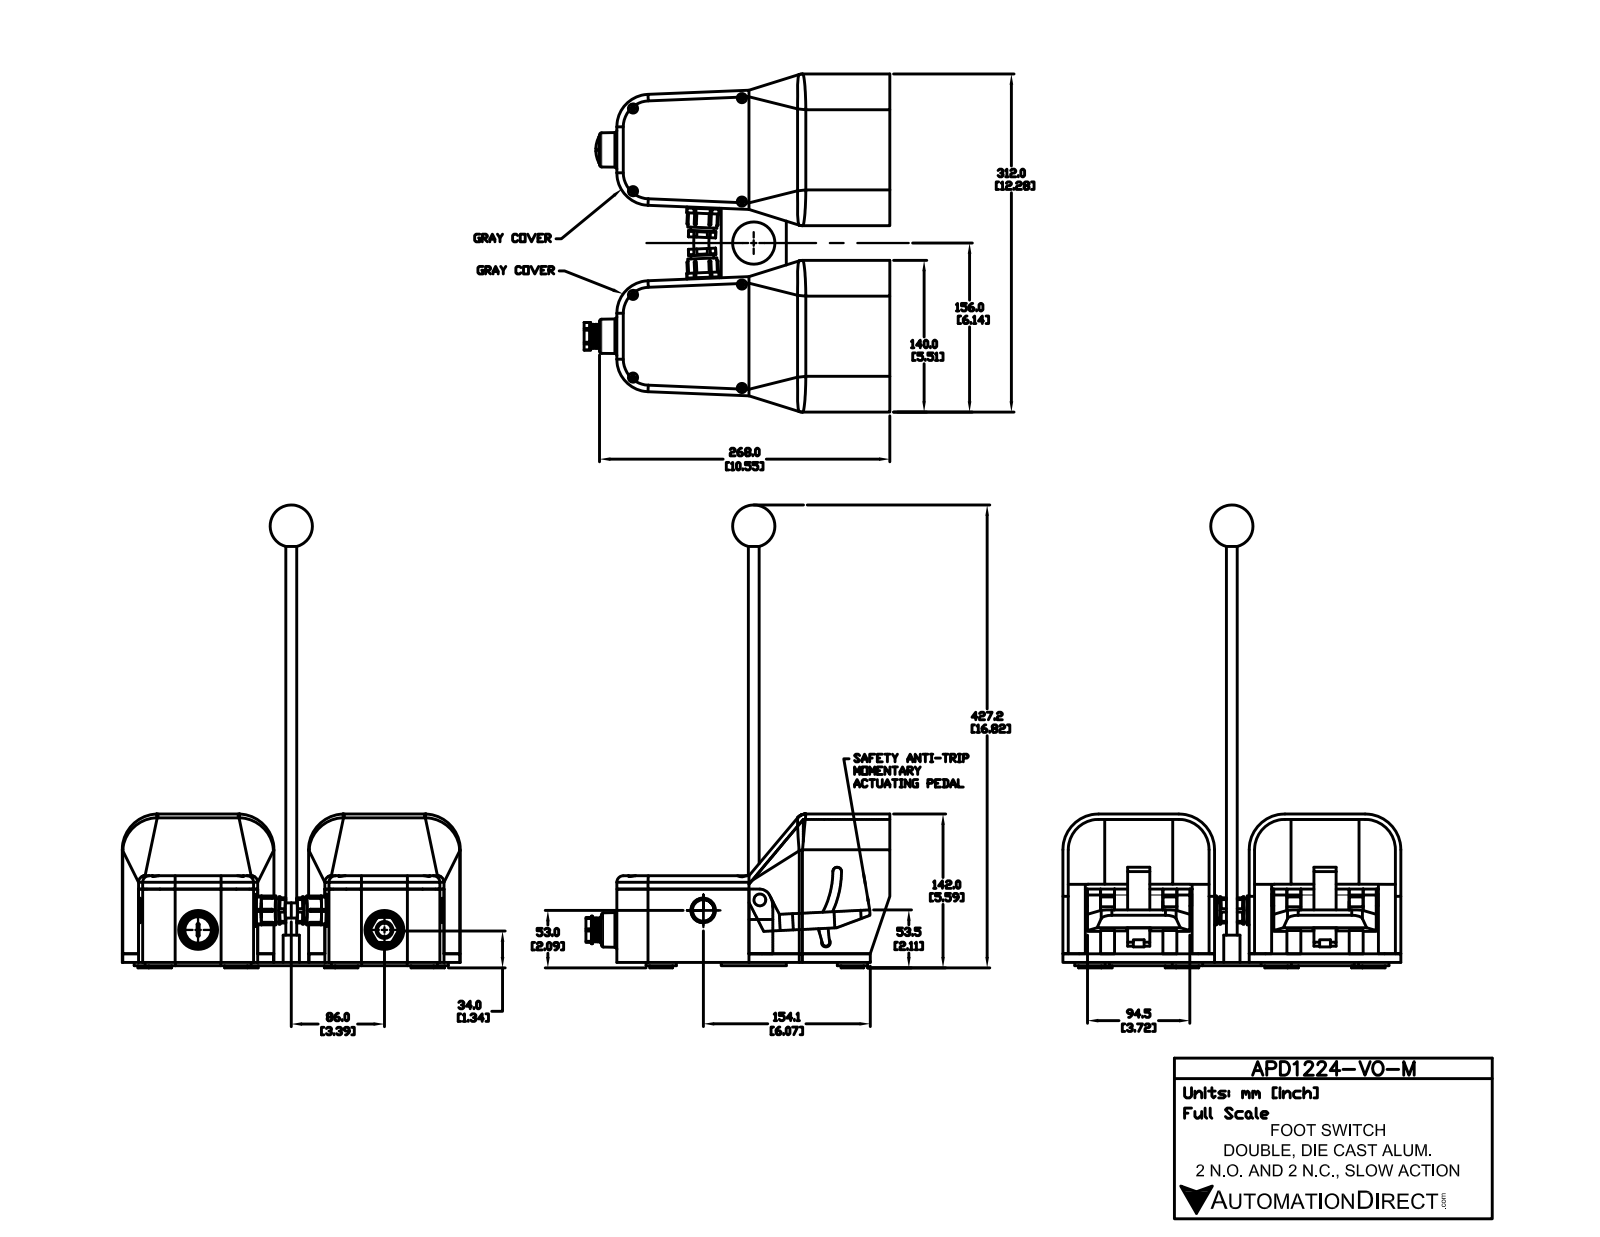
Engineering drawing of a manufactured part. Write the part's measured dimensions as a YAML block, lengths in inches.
part_name: "APD1224-V0-M"
step_written_by: "SolidWorks 2015 (AUTOMOTIVE_DESIGN)"
units: inches
bodies: {solids: 38, faces: 865, planar: 514, cylindrical: 237, other: 114}
overall_size: [16.817, 12.283, 11.112]
volume: 197.7
surface_area: 906.5
round_holes:
  - {diameter: 0.335, count: 8}
  - {diameter: 0.896, count: 4}
  - {diameter: 0.498, count: 1}
  - {diameter: 0.614, count: 1}
round_bosses_or_shafts:
  - {diameter: 1.102, count: 8}
  - {diameter: 0.827, count: 8}
  - {diameter: 0.782, count: 4}
  - {diameter: 1.171, count: 2}
  - {diameter: 1.051, count: 2}
  - {diameter: 0.992, count: 2}
  - {diameter: 0.846, count: 2}
  - {diameter: 1.004, count: 1}
partial_cylinders:
  - {radius: 0.039, count: 34}
  - {radius: 0.042, count: 12}
  - {radius: 0.394, count: 11}
  - {radius: 0.236, count: 5}
  - {radius: 1.102, count: 4}
  - {radius: 1.181, count: 4}
  - {radius: 1.299, count: 4}
  - {radius: 0.787, count: 2}
face_to_face_distances: [0.197, 5.315, 6.772, 0.315, 2.348, 5.512, 2.664, 2.349, 2.663, 0.118]
hole_center_spacings: [3.976, 5.206, 6.772, 3.004, 3.76, 5.211, 7.52, 8.172]
